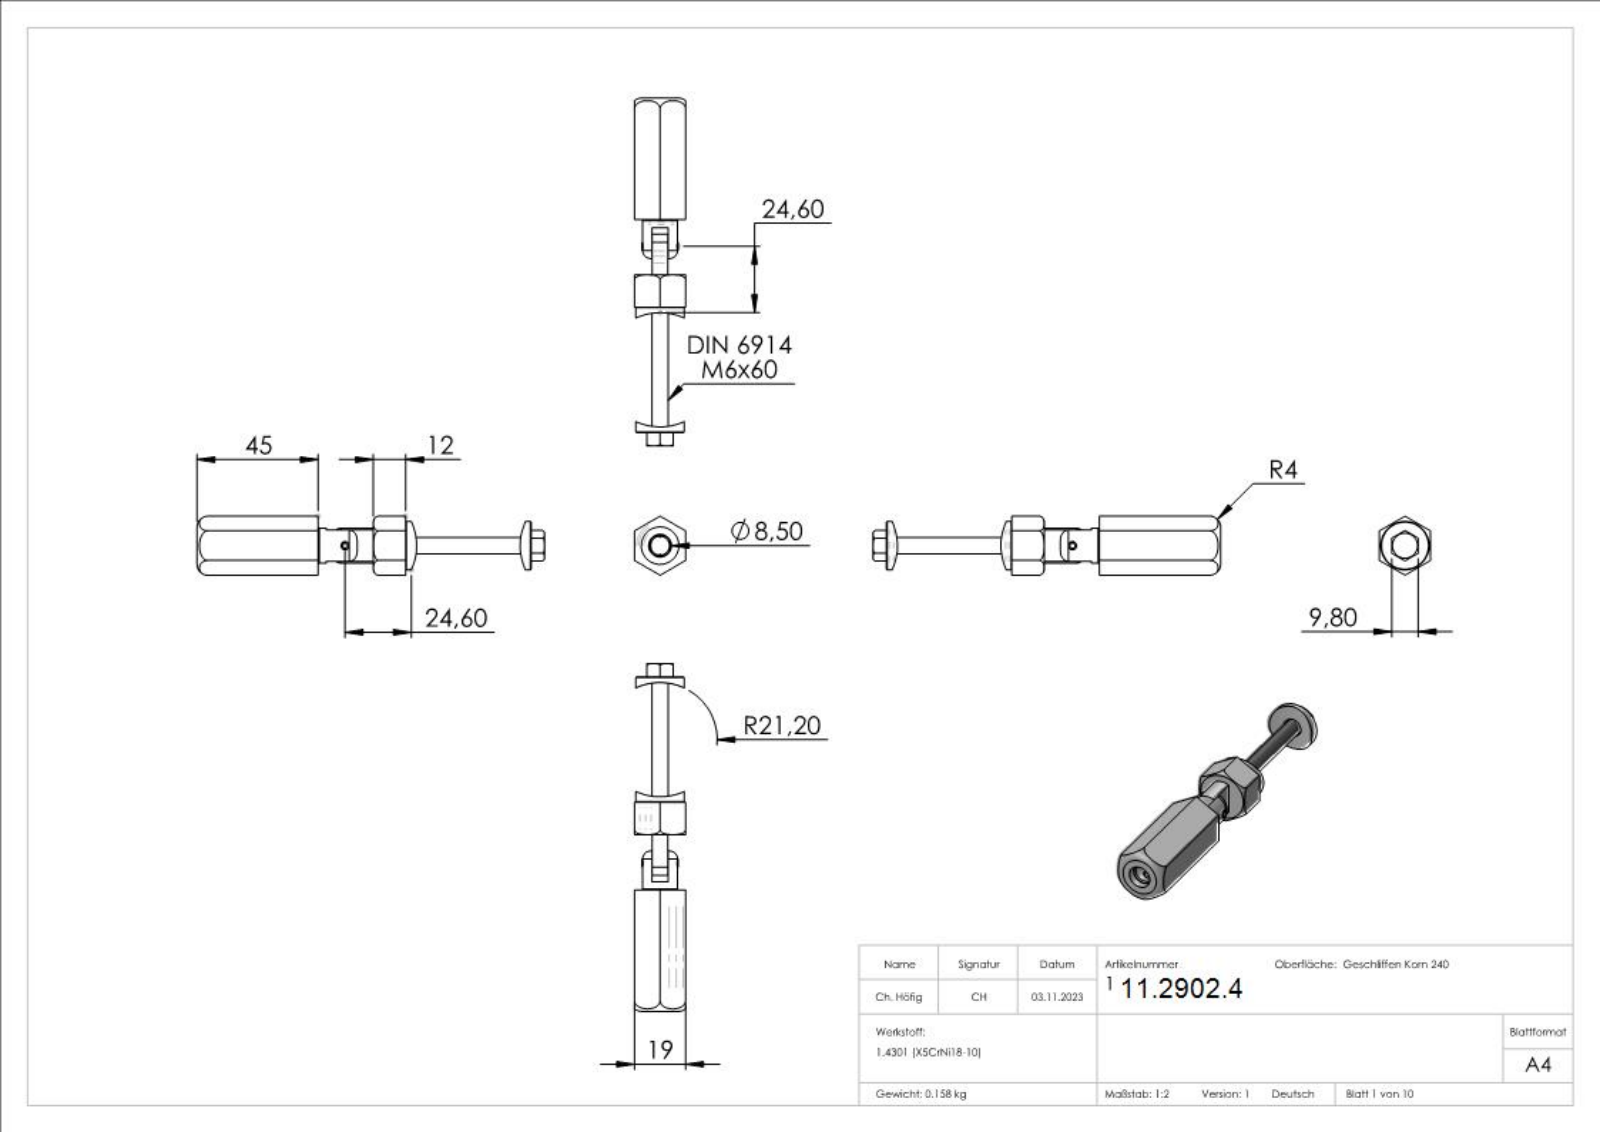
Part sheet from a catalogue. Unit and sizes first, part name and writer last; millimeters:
Units: millimetres
Overall size (bounding box): 129.12 × 21.94 × 19
Round holes (diameter × count): ⌀4.2 ×3, ⌀2 ×1, ⌀3.1 ×1, ⌀3.2 ×1, ⌀5 ×1, ⌀7 ×1, ⌀8.5 ×1
Round bosses / shafts (diameter × count): ⌀5 ×3, ⌀18 ×1, ⌀14 ×1, ⌀13 ×1, ⌀6 ×1, ⌀3 ×1
Partial cylindrical surfaces — rounded edges, fillets, slot ends (radius × count): R21.2 ×1
Main face-to-face distances: 19, 6.6, 12.4, 46.6, 6.5, 12.5, 5.9, 12, 58.6, 62.52
Hole centre spacings: 6, 12
Volume: 19 962 mm³ · Surface area: 13 610 mm²
Bodies: 11 solids, 339 faces (176 planar, 28 cylindrical, 135 other)
Part name (STEP PRODUCT): 10005400X Teil3_100054x06 Teil3; 10005400X Teil1_100054x06 Teil1; 10005400X Teil6_100054006 Teil6; 10005400X Teil4_100054006 Teil4 (+5 more)
STEP written by: SolidWorks 2018 (CONFIG_CONTROL_DESIGN)
